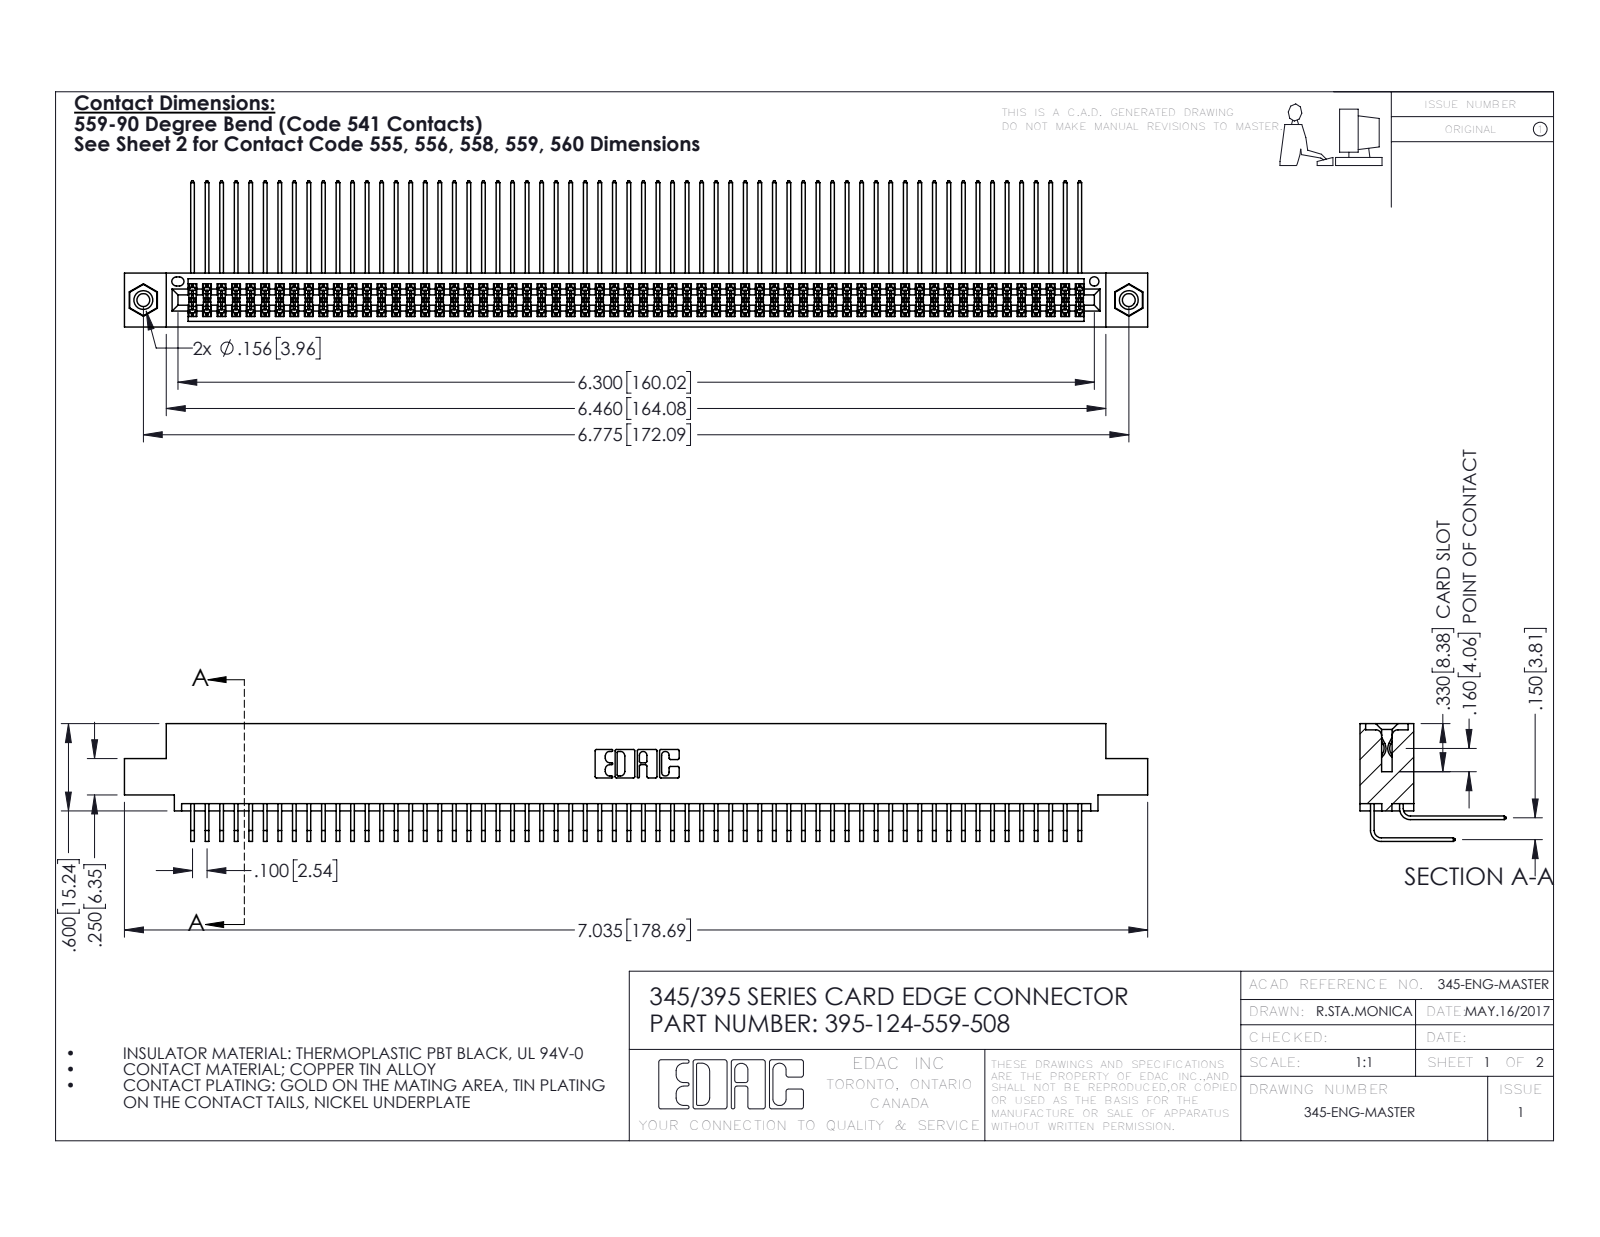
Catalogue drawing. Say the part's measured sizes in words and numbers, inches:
The part is named "345 Part_0.110 Offset - 0.156 Dia-TI; 345-292-001_559 Tail - 2; 395-124-559-508; 345-292-001_558 559 Tail - 1 (+1 more)". Its 3-D file was written by "SolidWorks 2016 (CONFIG_CONTROL_DESIGN)". It is 127 solids with 6638 faces: 4456 planar, 2166 cylindrical and 16 other. Overall it measures 7.035 by 1.005 by 0.809 inches. Its volume is 1.109 cubic inches and its surface area 47.63 square inches. Round holes: 2 of diameter 0.089, 2 of diameter 0.125, 2 of diameter 0.156, 1 of diameter 0.064. Round bosses or shafts: 2 of diameter 0.155. Partial cylindrical surfaces (rounded edges, fillets, slot ends): 186 of radius 0.006, 22 of radius 0.01, 6 of radius 0.007, 6 of radius 0.031, 3 of radius 0.026, 2 of radius 0.014, 2 of radius 0.019, 2 of radius 0.022. The main face-to-face distances are 0.072, 0.298, 0.2, 0.37, 0.098, 0.272, 0.025, 0.225, 0.175, 0.15. The hole center spacings are 0.27, 6.539, 6.775.
